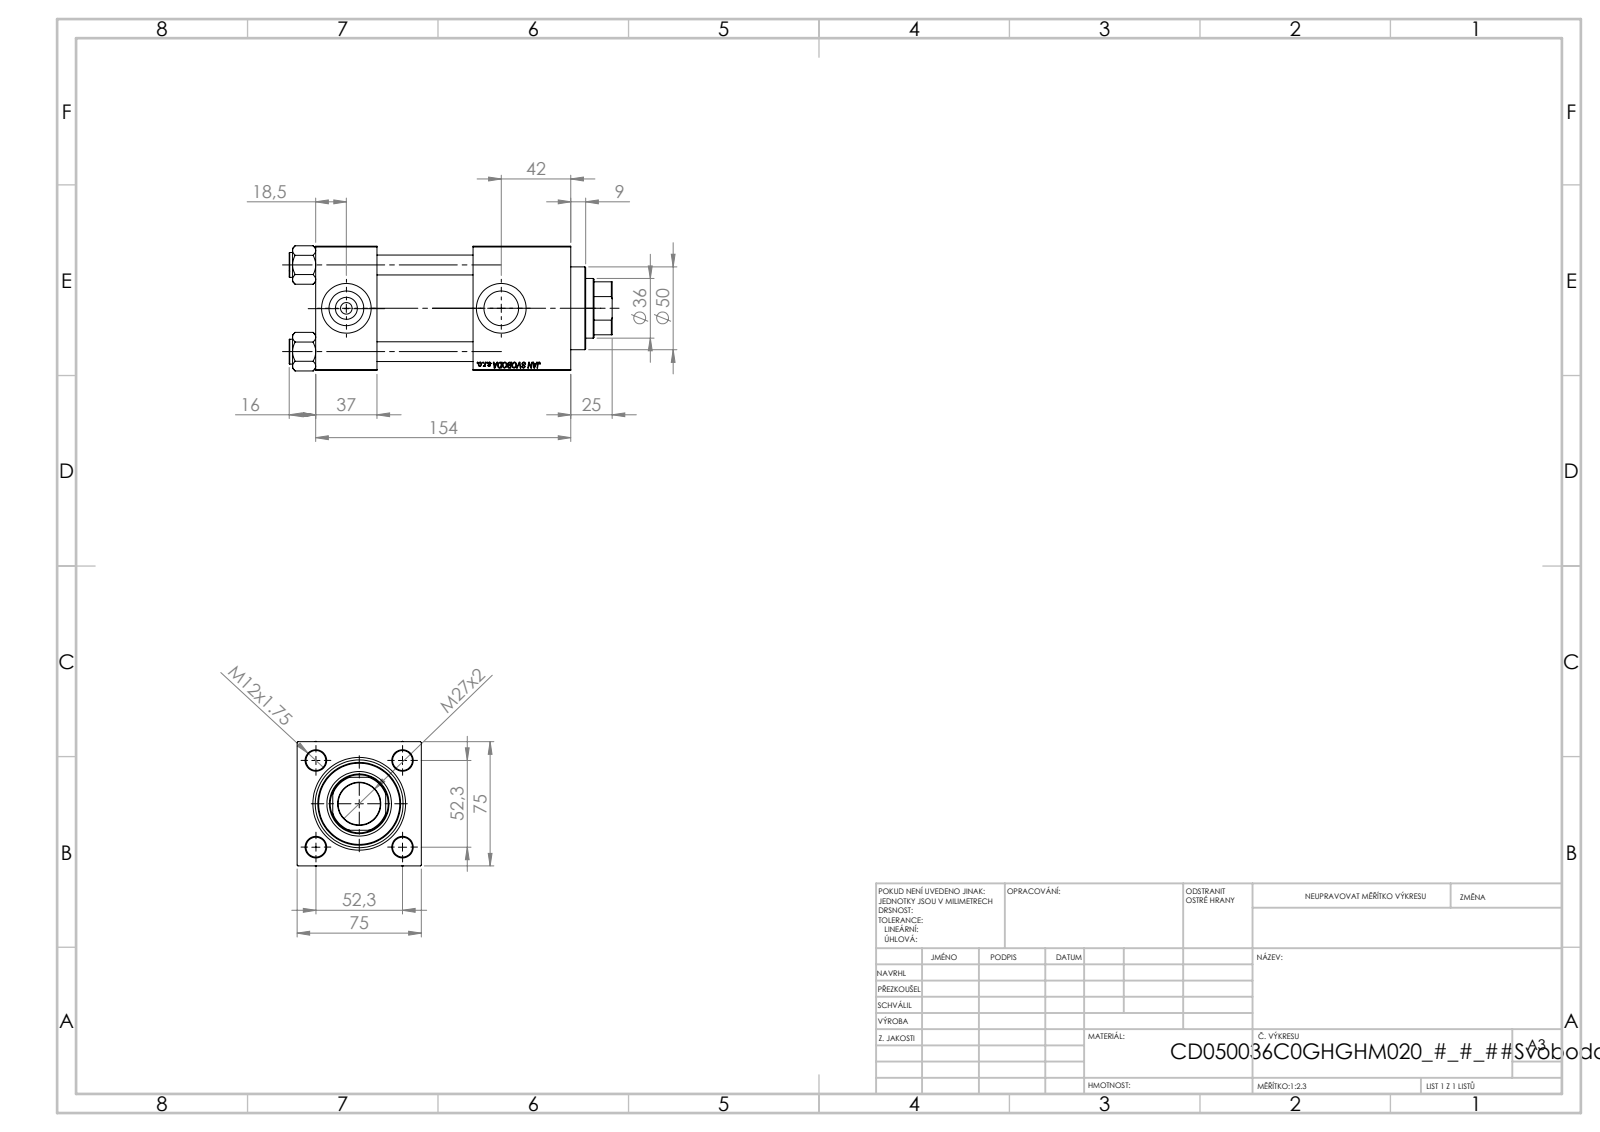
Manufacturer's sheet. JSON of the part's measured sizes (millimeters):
{"part_name": "V215CD_C_TYCINKA; V215CD_Body_C; V215CD_VC_C; NUT_M5_V215CD_C (+1 more)", "step_written_by": "SolidWorks 2019 (CONFIG_CONTROL_DESIGN)", "units": "millimeters", "bodies": {"solids": 11, "faces": 1148, "planar": 526, "cylindrical": 86, "other": 536}, "overall_size": [195, 75.54, 75], "volume_mm3": 686044, "surface_area_mm2": 155490, "round_holes": [[12, 4], [7, 2], [20.96, 2], [30, 2], [25.5, 1], [36, 1], [39, 1], [41, 1], [53, 1]], "round_bosses_or_shafts": [[15, 4], [56, 1], [50, 1]], "partial_cylinders_radius": [[17.5, 1]], "face_to_face_distances": [75, 37, 95, 58, 154, 117, 59, 125.3, 88.3, 30.3], "hole_center_spacings": [36.98, 52.3, 73.96, 93.5]}
